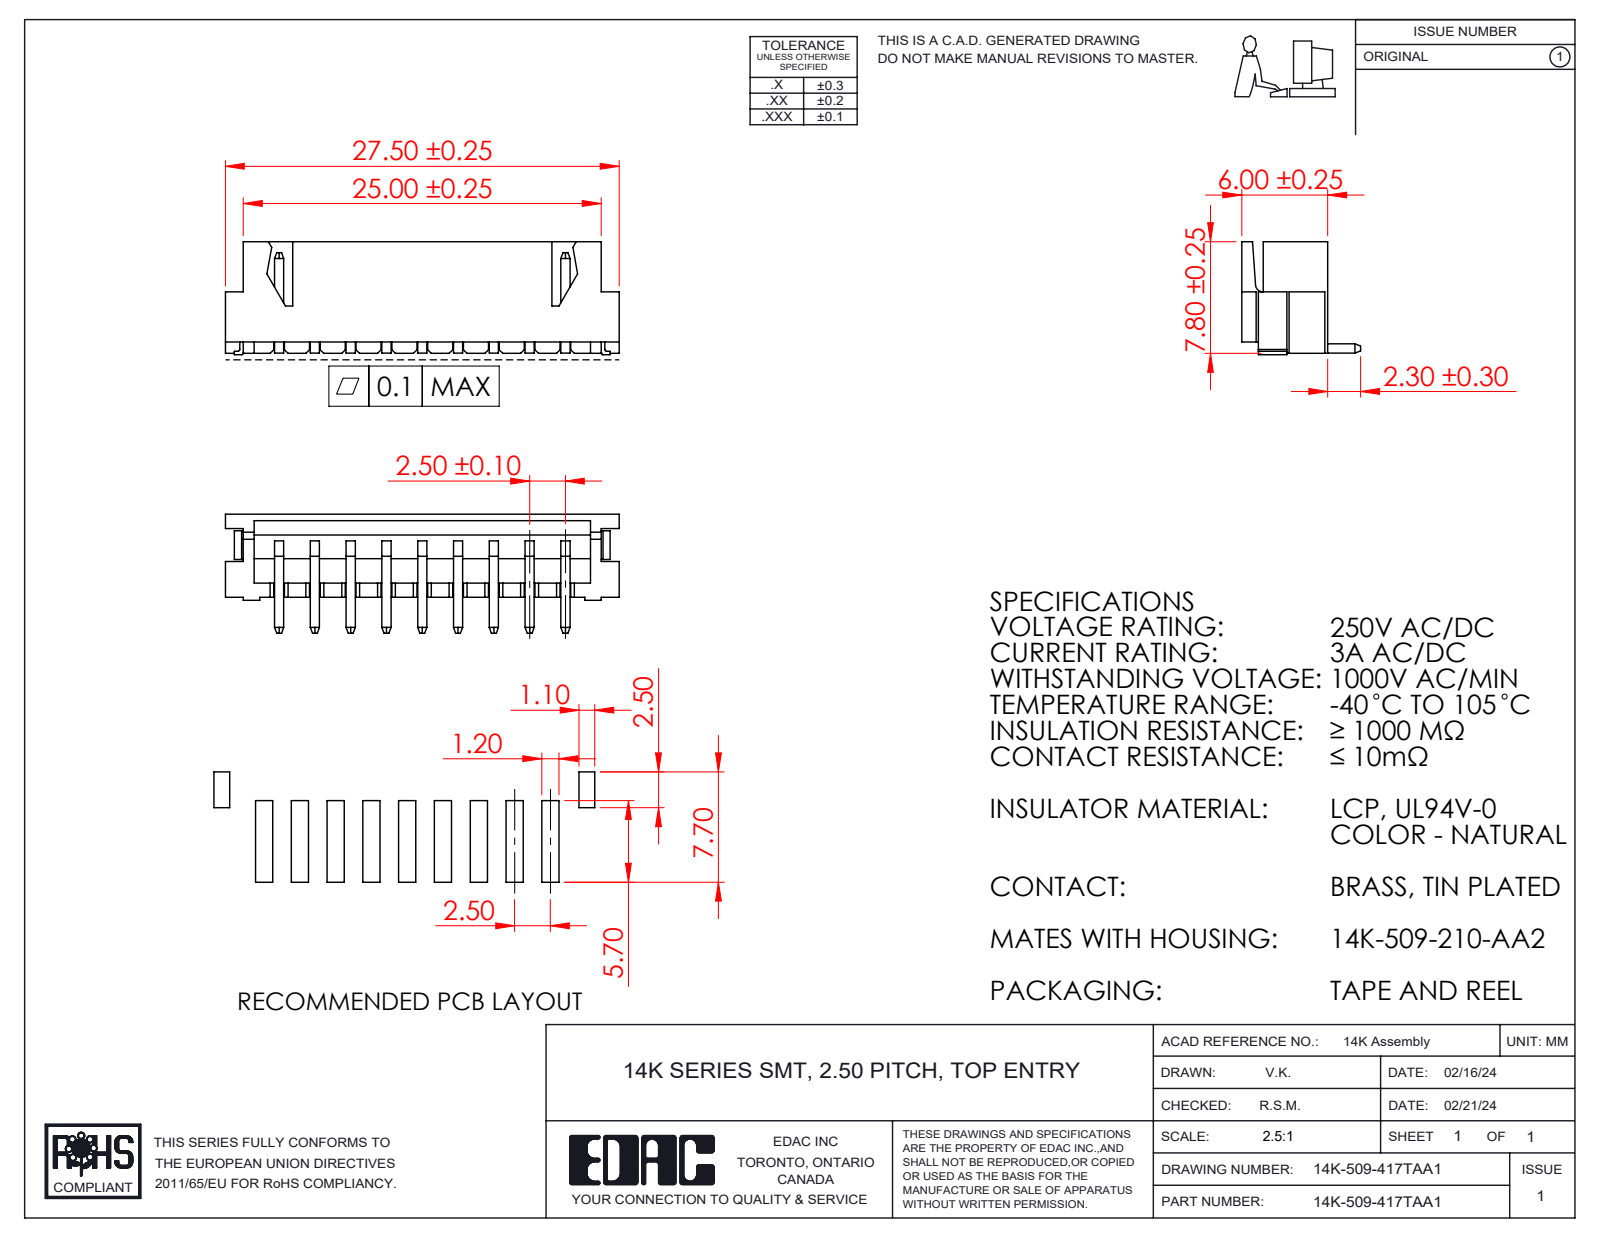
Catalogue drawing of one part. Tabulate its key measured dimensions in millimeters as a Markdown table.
| quantity | value |
| --- | --- |
| part name | 14K Series SMT Top Entry Insulator_509; 14K-509-418TAA1; 14K Series SMT Pin_Top Entry |
| STEP written by | SolidWorks 2023 (CONFIG_CONTROL_DESIGN) |
| units | millimeters |
| bodies | 10 solids, 478 faces (436 planar, 42 cylindrical, 0 other) |
| overall size | 27.5 × 8.3 × 7.9 |
| volume | 496 mm³ |
| surface area | 1 566 mm² |
| partial cylindrical surfaces (radius × count) | 0.38 × 18, 0.12 × 4, 0.43 × 1, 0.5 × 1, 1.07 × 1 |
| main face-to-face distances | 0.75, 5.05, 5.8, 2.5, 0.64, 4.3, 1, 5, 1.25, 1.86 |
